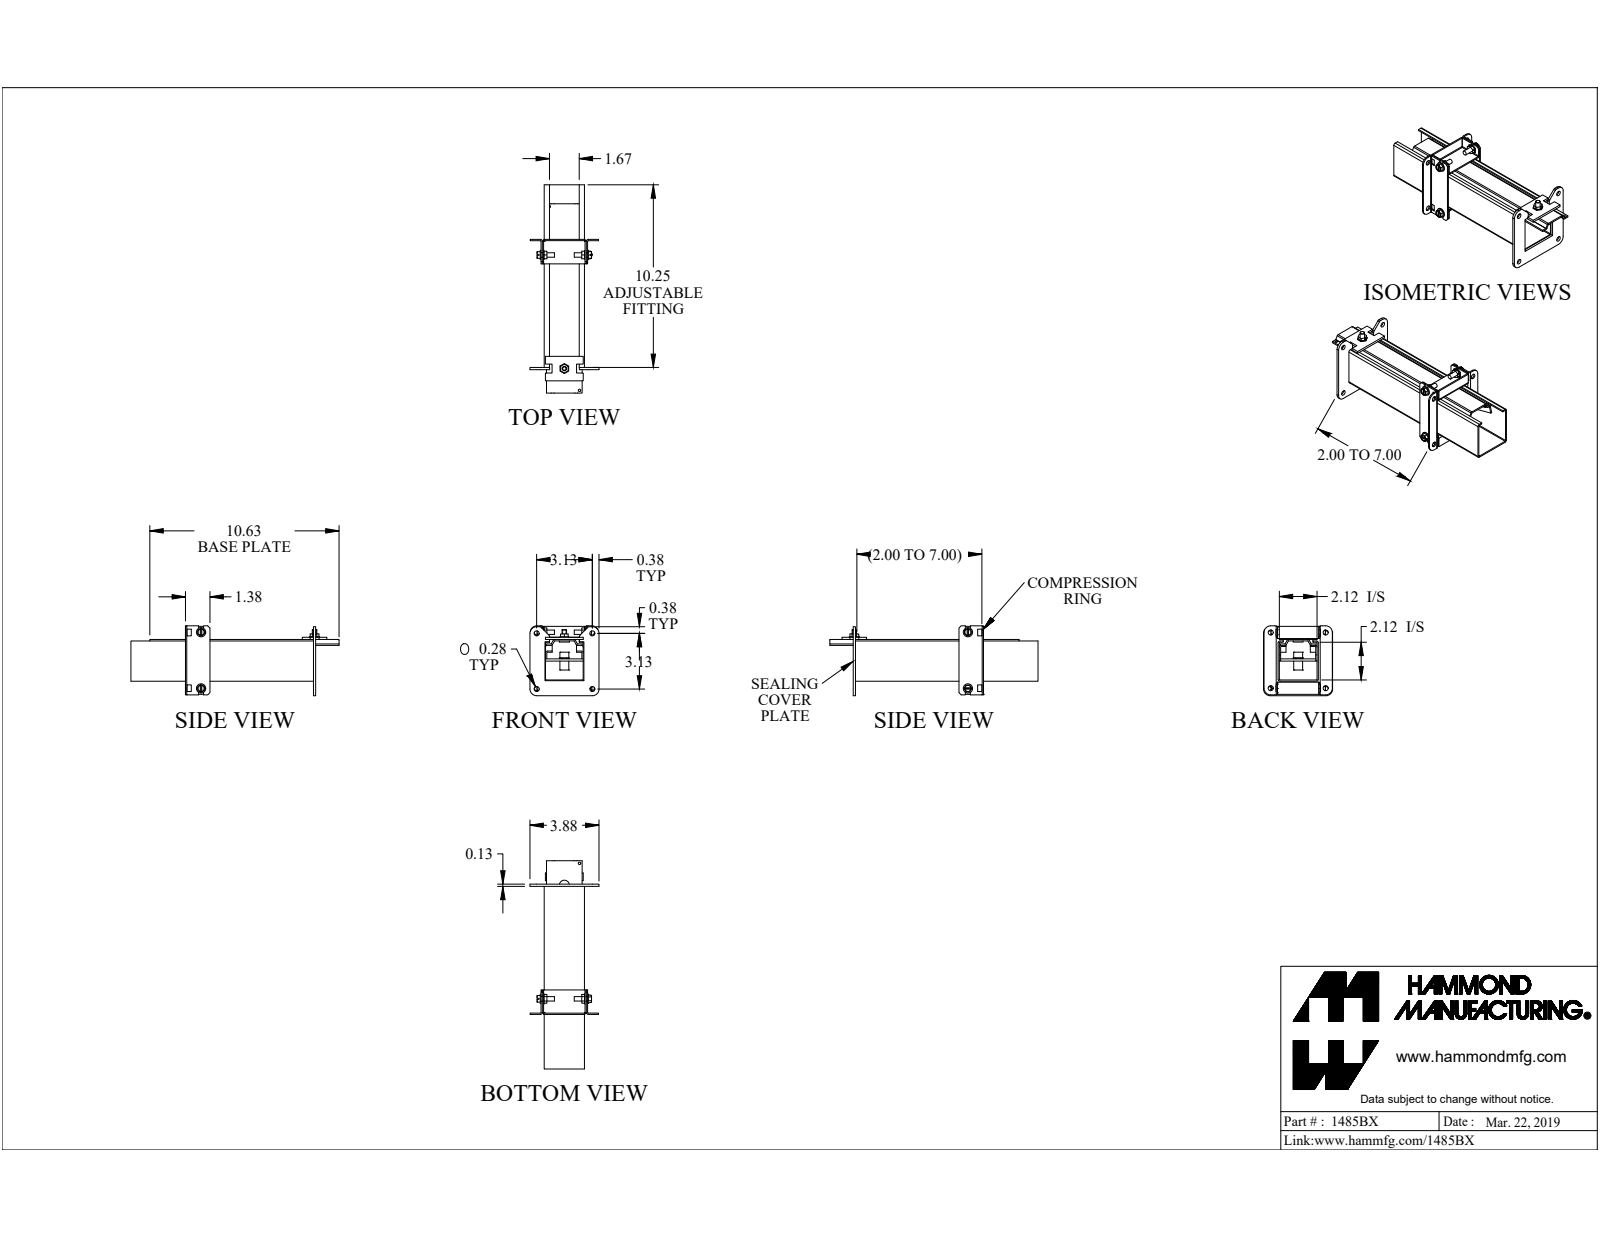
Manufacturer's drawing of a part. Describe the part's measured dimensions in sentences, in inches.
The part is named "1485BX". Its 3-D file was written by "SolidWorks 2019 (CONFIG_CONTROL_DESIGN)". It is 19 solids with 426 faces: 304 planar, 89 cylindrical and 33 other. Overall it measures 11.688 by 3.924 by 3.875 inches. Its volume is 10.78 cubic inches and its surface area 290 square inches. Round holes: 10 of diameter 0.281, 3 of diameter 0.196, 2 of diameter 0.14, 2 of diameter 0.35, 1 of diameter 0.265, 1 of diameter 0.313. Round bosses or shafts: 2 of diameter 0.52, 2 of diameter 0.246, 1 of diameter 0.563, 1 of diameter 0.25. Partial cylindrical surfaces (rounded edges, fillets, slot ends): 13 of radius 0.036, 13 of radius 0.108, 8 of radius 0.375, 4 of radius 0.004, 4 of radius 0.085, 4 of radius 0.125. The main face-to-face distances are 0.072, 2.188, 2.116, 2.26, 0.081, 0.177, 2.365, 2.293, 0.105, 2.343. The hole center spacings are 3.125, 3.076, 3.086, 3.098, 3.113, 3.125, 3.174, 4.392.
